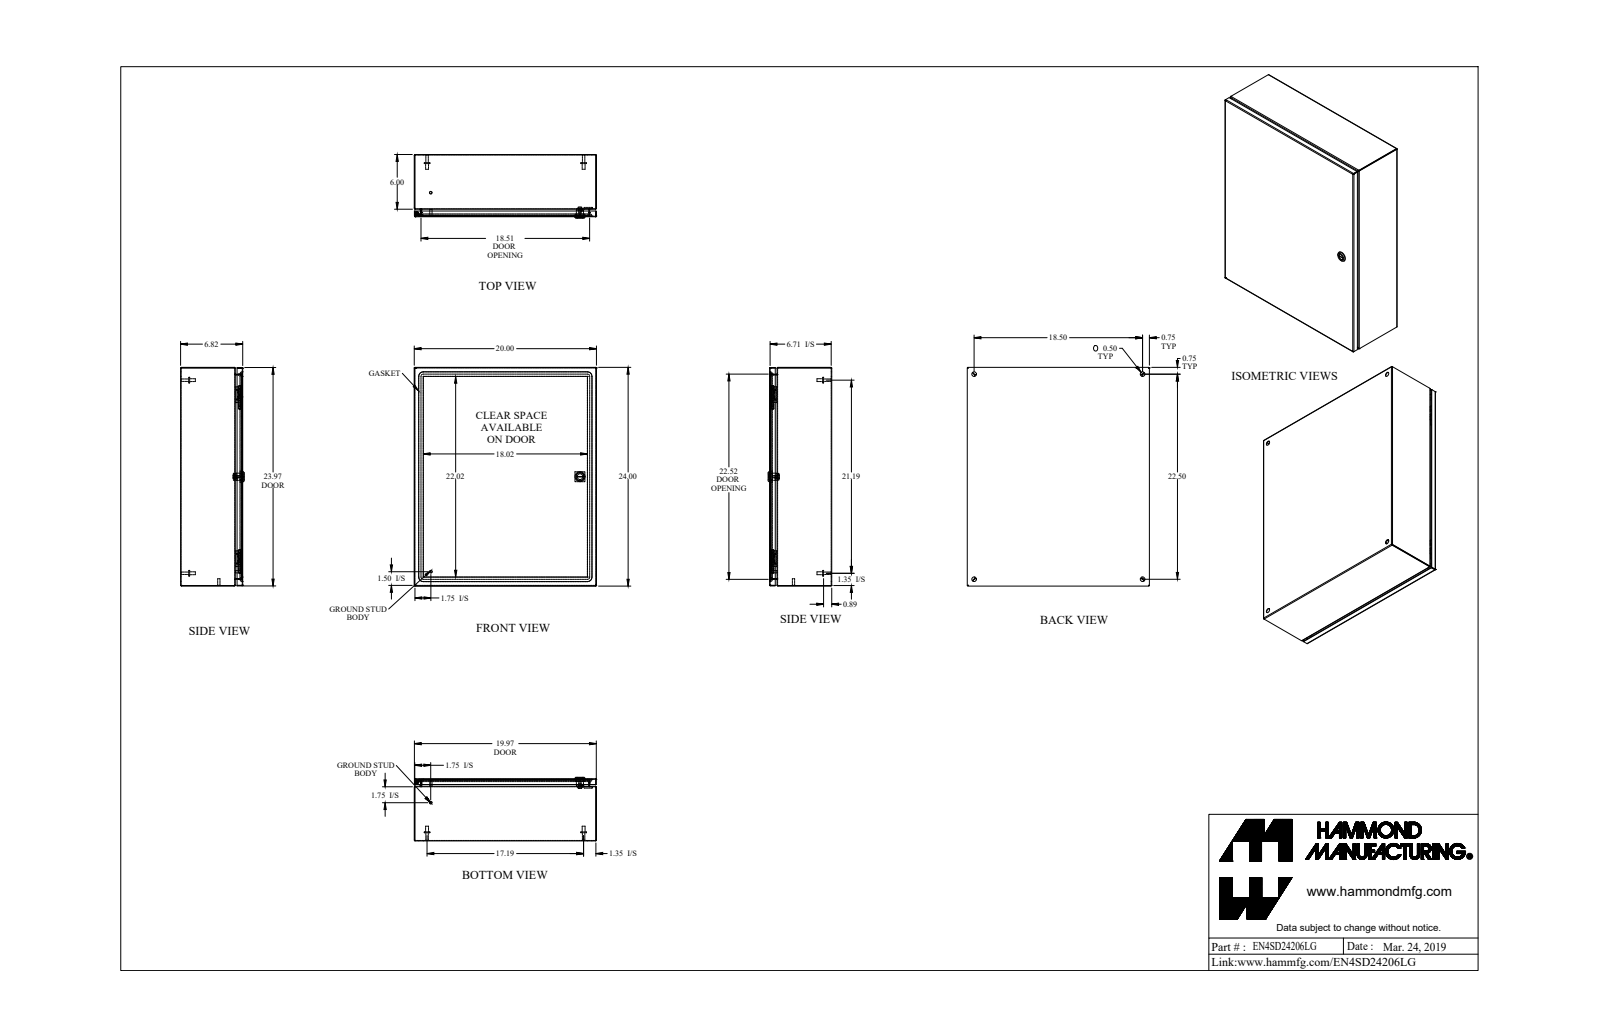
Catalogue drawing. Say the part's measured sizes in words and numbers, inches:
The part is named "EN4SD24206LG_Default". Its 3-D file was written by "SolidWorks 2019 (CONFIG_CONTROL_DESIGN)". It is 21 solids with 634 faces: 285 planar, 213 cylindrical and 136 other. Overall it measures 24 by 20 by 6.982 inches. Its volume is 103.2 cubic inches and its surface area 3 513 square inches. Round holes: 4 of diameter 0.5, 1 of diameter 0.172, 1 of diameter 0.232, 1 of diameter 0.24, 1 of diameter 0.242, 1 of diameter 0.625, 1 of diameter 0.785. Round bosses or shafts: 4 of diameter 0.625, 4 of diameter 0.313, 4 of diameter 0.27, 2 of diameter 0.281, 2 of diameter 0.25, 1 of diameter 1.1, 1 of diameter 0.525, 1 of diameter 0.455. Partial cylindrical surfaces (rounded edges, fillets, slot ends): 21 of radius 0.029, 21 of radius 0.086, 16 of radius 0.25, 8 of radius 19, 4 of radius 0.006, 4 of radius 0.062, 4 of radius 0.499, 2 of radius 0.125. The main face-to-face distances are 0.057, 6.765, 6.708, 6.822, 19.943, 23.943, 19.886, 20, 23.886, 24. The hole center spacings are 18.5, 22.5, 29.129, 11.299, 11.3, 20.754, 20.755.
